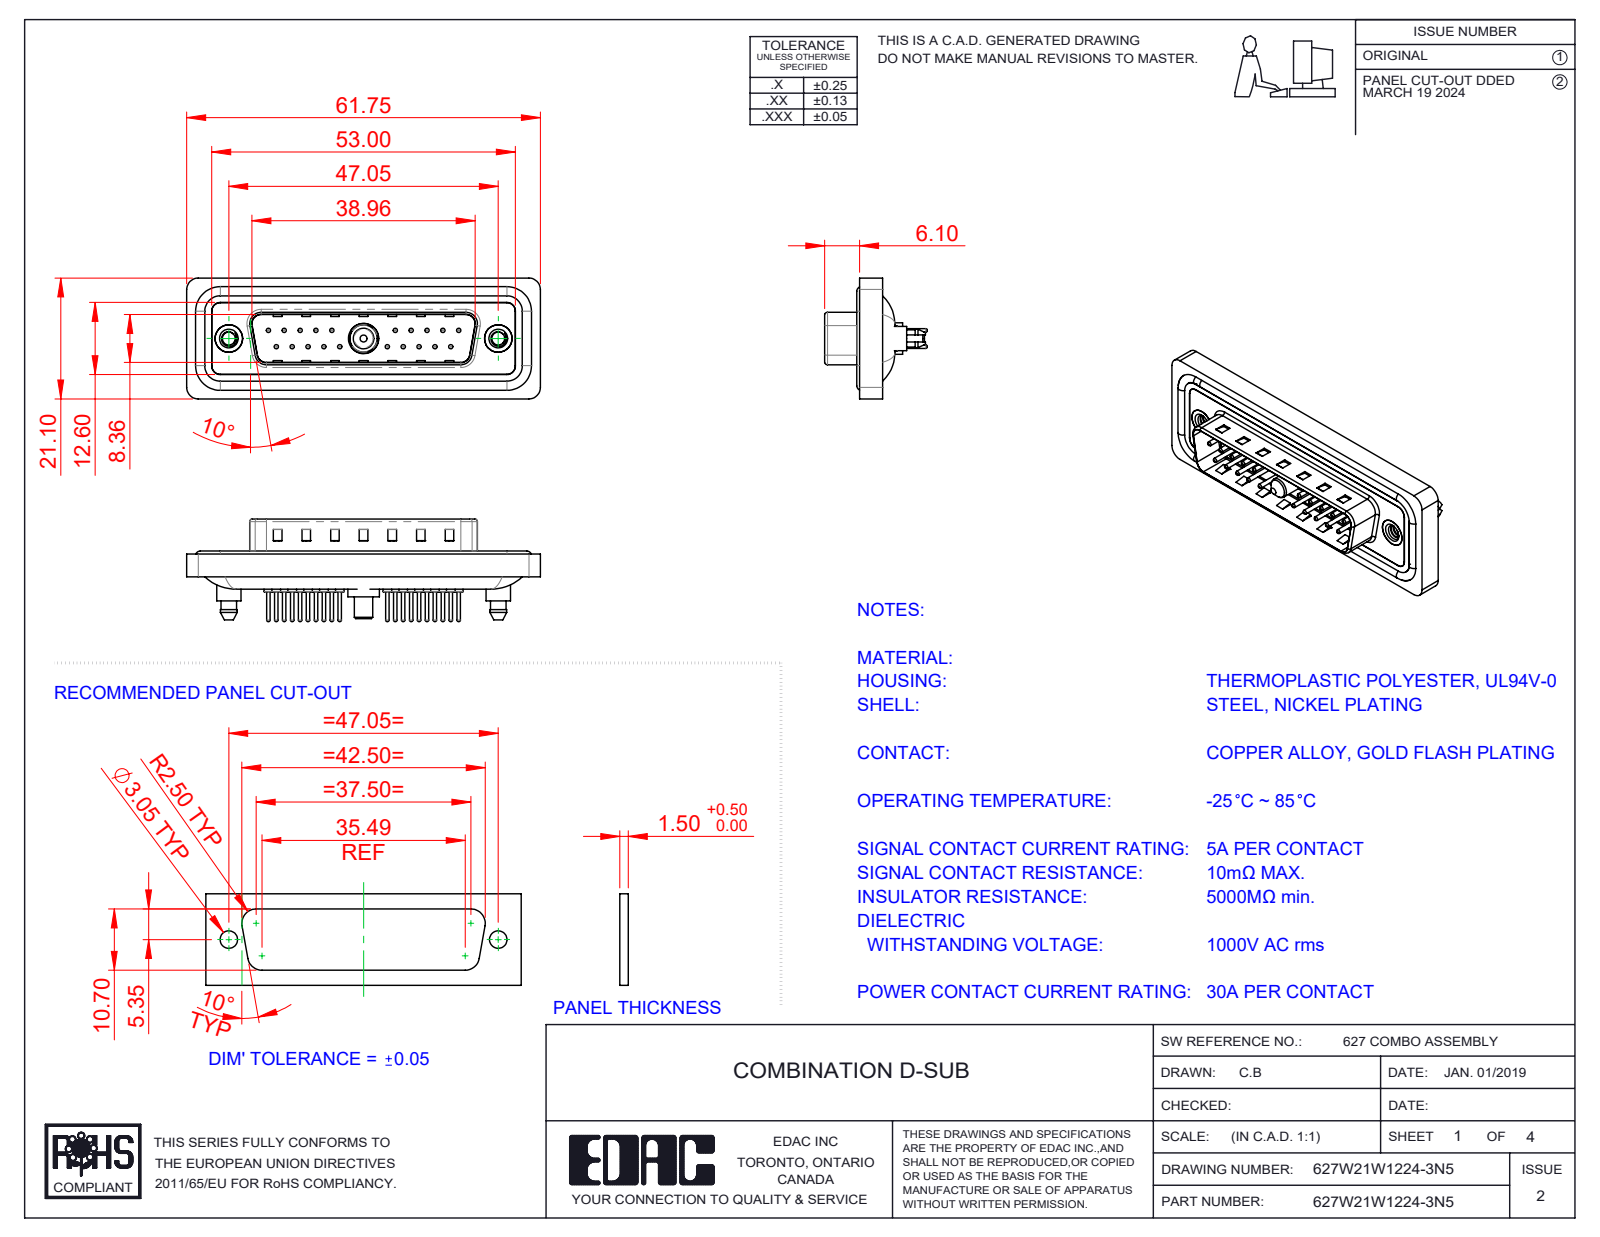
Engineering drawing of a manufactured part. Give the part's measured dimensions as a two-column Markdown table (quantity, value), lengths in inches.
| quantity | value |
| --- | --- |
| part name | Power Pin_30A S; 627W21W1224-3N5; 627Combo Contact Row 1_24; 627Combo Contact Row 2_24 (+5 more) |
| STEP written by | SolidWorks 2023 (CONFIG_CONTROL_DESIGN) |
| units | inches |
| bodies | 29 solids, 1312 faces (375 planar, 519 cylindrical, 418 other) |
| overall size | 2.431 × 0.831 × 0.705 |
| volume | 0.448 in³ |
| surface area | 19.05 in² |
| round holes (diameter × count) | 0.03 × 20, 0.063 × 20, 0.079 × 20, 0.089 × 2, 0.157 × 2, 0.189 × 2, 0.197 × 2, 0.191 × 1, 0.209 × 1 |
| round bosses / shafts (diameter × count) | 0.059 × 20, 0.024 × 20, 0.063 × 4, 0.213 × 2, 0.193 × 2, 0.167 × 2, 0.217 × 1, 0.205 × 1 |
| partial cylindrical surfaces (radius × count) | 0.059 × 24, 0.079 × 18, 0.063 × 10, 0.02 × 8, 0.01 × 4, 0.024 × 4, 0.026 × 4, 0.035 × 4 |
| main face-to-face distances | 0.016, 0.059, 0.043, 0.063, 0.02, 0.122, 0.114, 0.161, 0.032, 0.377 |
| hole center spacings | 0.124, 0.109, 0.218, 0.327, 0.198, 0.763, 0.826, 0.872 |
